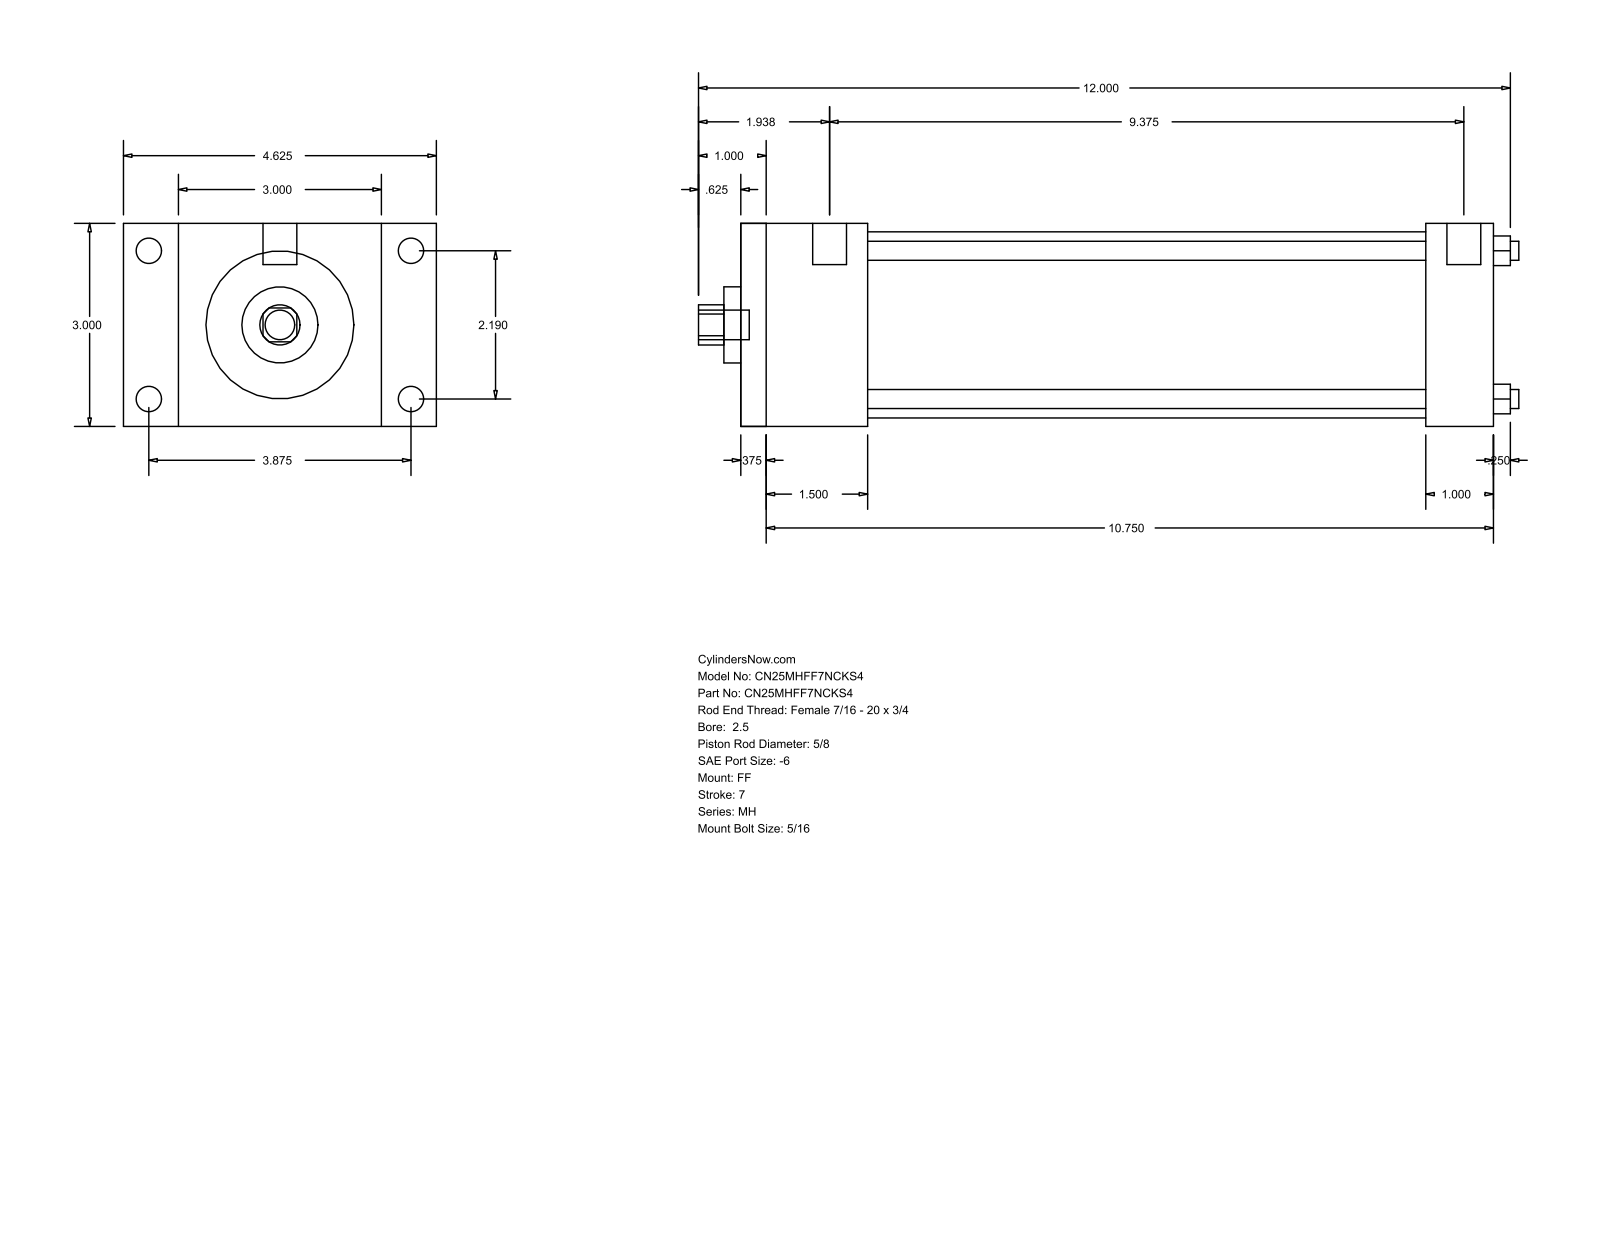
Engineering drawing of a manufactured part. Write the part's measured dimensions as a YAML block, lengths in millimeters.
part_name: "MH_FF__0250_0.625"
step_written_by: "GSSL Pune (CONFIG_CONTROL_DESIGN)"
units: millimeters
bodies: {solids: 0, faces: 92, planar: 64, cylindrical: 28, other: 0}
overall_size: [307.98, 117.47, 76.2]
round_holes:
  - {diameter: 7.14, count: 4}
  - {diameter: 15.88, count: 1}
  - {diameter: 28.57, count: 1}
  - {diameter: 69.85, count: 1}
round_bosses_or_shafts:
  - {diameter: 9.53, count: 4}
  - {diameter: 5.56, count: 4}
  - {diameter: 12.7, count: 2}
  - {diameter: 11.11, count: 1}
partial_cylinders:
  - {radius: 7.54, count: 1}
face_to_face_distances: [76.2, 282.57, 9.52, 273.05, 25.4, 47.62, 257.17, 38.1, 247.65, 209.55]
hole_center_spacings: [39.33, 55.62, 78.66]
